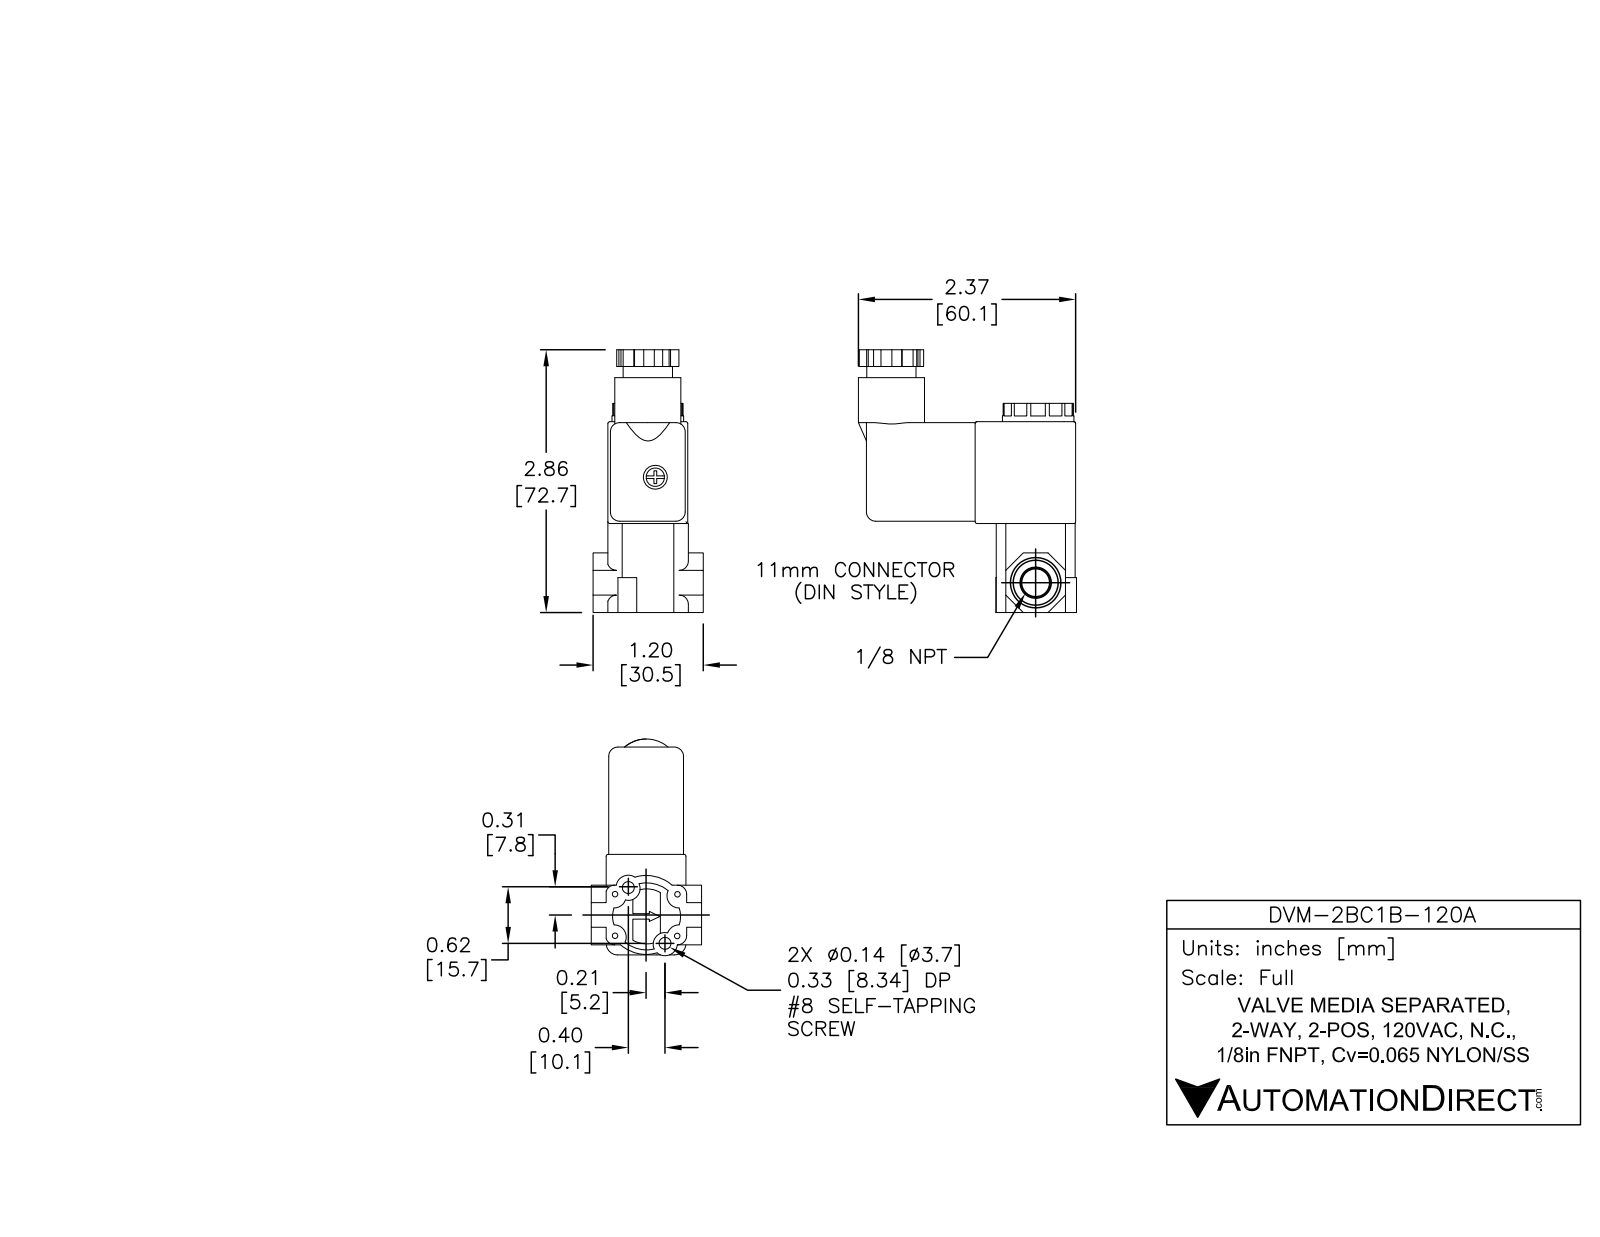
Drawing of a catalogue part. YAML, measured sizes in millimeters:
part_name: "DVM-2BC1B-120A"
step_written_by: "SolidWorks 2015 (AUTOMOTIVE_DESIGN)"
units: millimeters
bodies: {solids: 1, faces: 253, planar: 133, cylindrical: 101, other: 19}
overall_size: [74, 63.1, 22.3]
volume: 49850
surface_area: 12840
round_holes:
  - {diameter: 3.2, count: 2}
  - {diameter: 3.5, count: 2}
  - {diameter: 3.5, count: 2}
  - {diameter: 8.1, count: 2}
  - {diameter: 6.4, count: 1}
  - {diameter: 6.6, count: 1}
  - {diameter: 10.4, count: 1}
round_bosses_or_shafts:
  - {diameter: 19.8, count: 1}
  - {diameter: 18.3, count: 1}
  - {diameter: 13.6, count: 1}
  - {diameter: 6.4, count: 1}
  - {diameter: 5.1, count: 1}
partial_cylinders:
  - {radius: 3.9, count: 12}
  - {radius: 0.5, count: 11}
  - {radius: 2.5, count: 11}
  - {radius: 3.4, count: 4}
  - {radius: 3.2, count: 2}
  - {radius: 3.3, count: 2}
  - {radius: 3.4, count: 2}
  - {radius: 7, count: 2}
face_to_face_distances: [0.7, 21.4, 22.1, 20.7, 57.2, 16.5, 5.1, 54.1, 33.9, 28.8]
hole_center_spacings: [11.4, 48.1, 4.4, 4.4, 8.6, 9.7, 9.7, 10]
